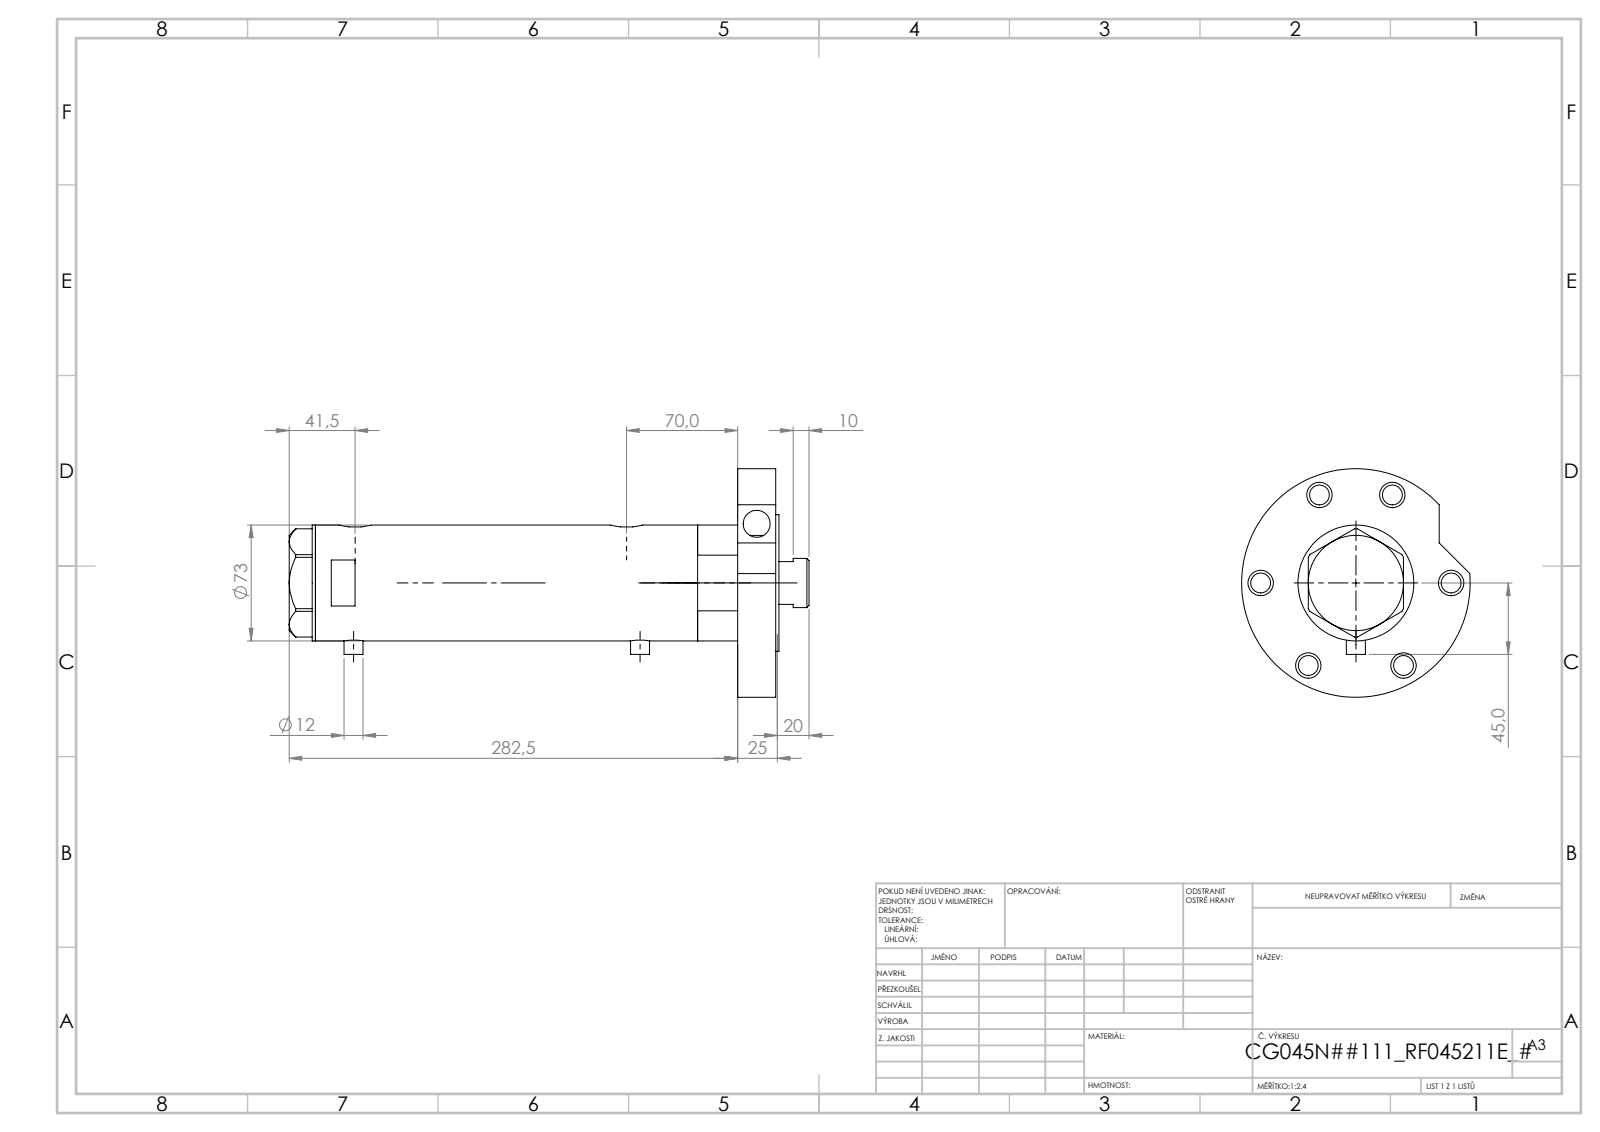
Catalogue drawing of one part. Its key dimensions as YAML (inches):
part_name: "V270CG_MIDDLE; V270CG_BACK; V270CG_FRONT; V270CG_VC (+1 more)"
step_written_by: "SolidWorks 2019 (CONFIG_CONTROL_DESIGN)"
units: inches
bodies: {solids: 5, faces: 169, planar: 61, cylindrical: 88, other: 20}
overall_size: [11.91, 5.669, 5.669]
volume: 80.43
surface_area: 348.4
round_holes:
  - {diameter: 0.492, count: 8}
  - {diameter: 0.63, count: 6}
  - {diameter: 0.197, count: 2}
  - {diameter: 0.518, count: 2}
  - {diameter: 0.413, count: 1}
  - {diameter: 0.669, count: 1}
  - {diameter: 1.26, count: 1}
  - {diameter: 1.319, count: 1}
  - {diameter: 1.772, count: 1}
  - {diameter: 1.89, count: 1}
  - {diameter: 2.362, count: 1}
  - {diameter: 2.52, count: 1}
round_bosses_or_shafts:
  - {diameter: 0.472, count: 2}
  - {diameter: 5.669, count: 1}
  - {diameter: 3.386, count: 1}
  - {diameter: 2.874, count: 1}
  - {diameter: 2.283, count: 1}
  - {diameter: 1.22, count: 1}
partial_cylinders:
  - {radius: 0.394, count: 2}
face_to_face_distances: [0.945, 9.388, 1.024, 10.333, 0.079, 10.411, 7.013, 2.374, 3.319, 5.99]
hole_center_spacings: [2.362, 2.625, 3.928, 4.091, 4.237, 4.714, 6.404, 0.039]
